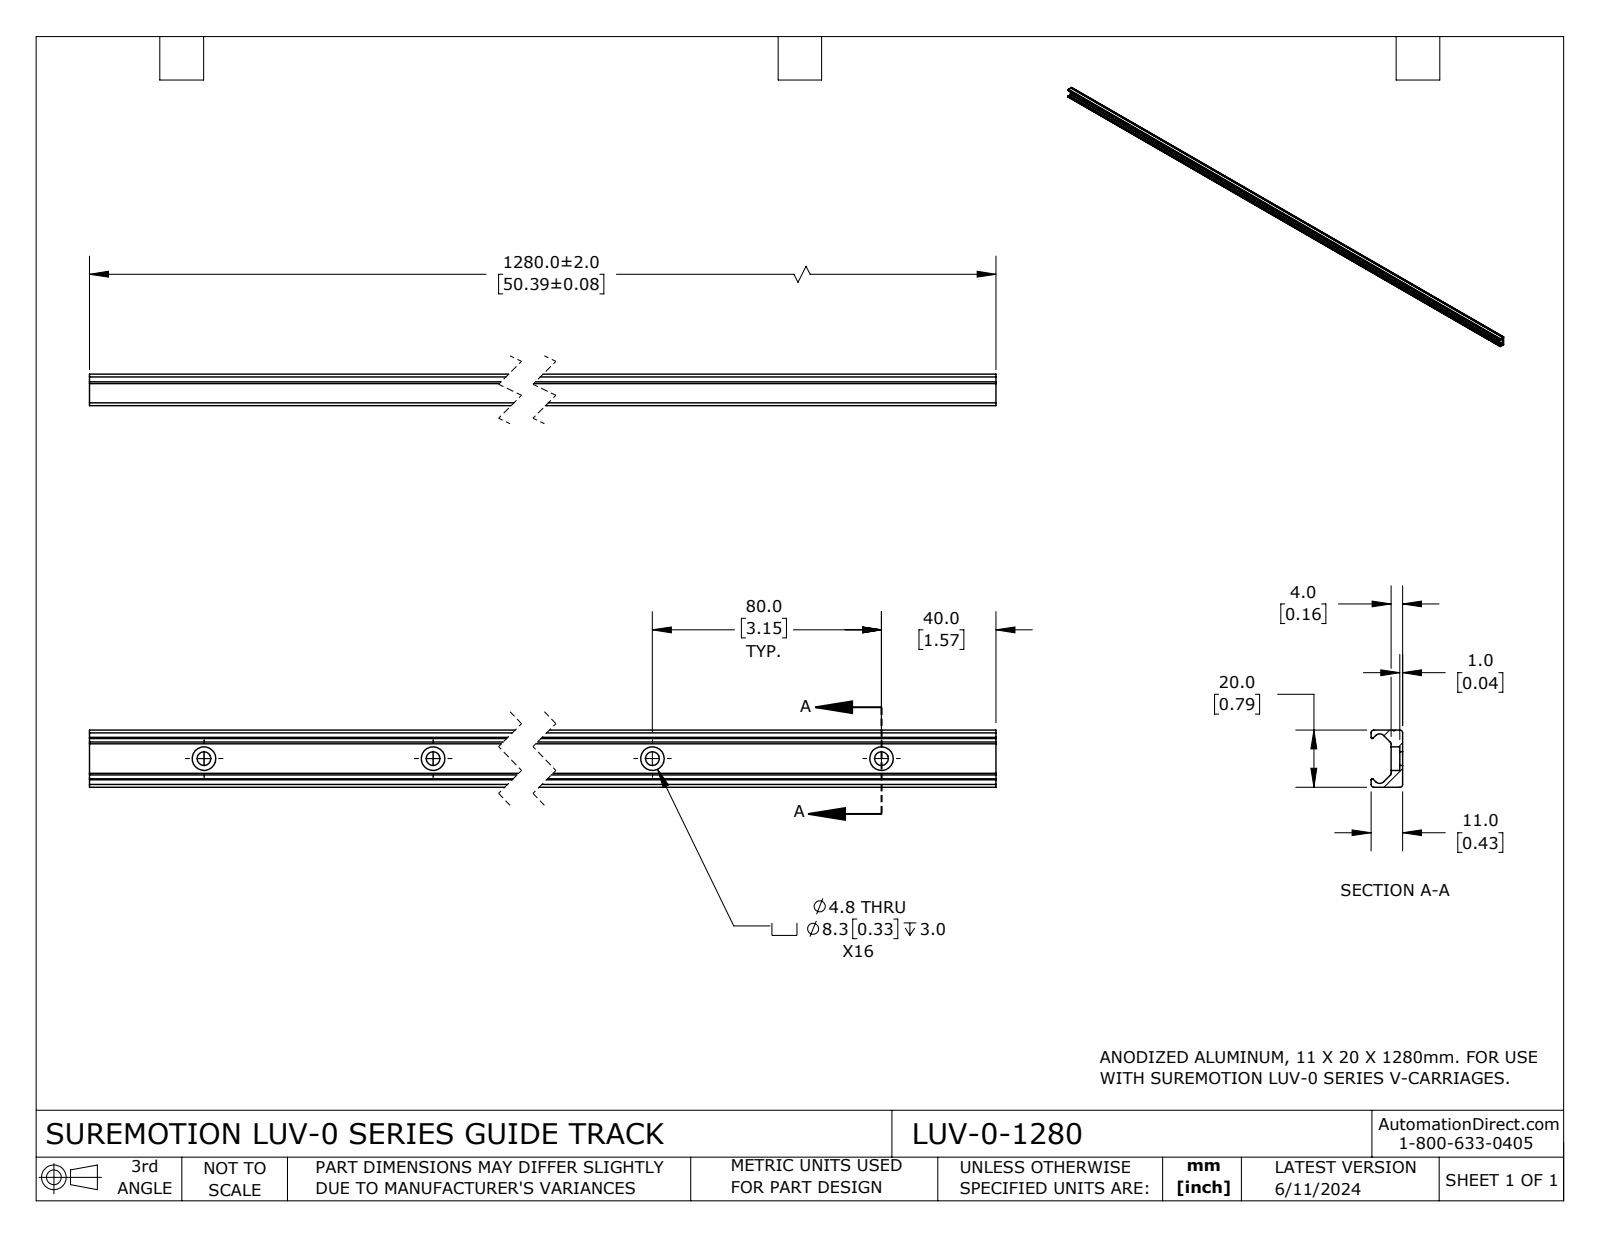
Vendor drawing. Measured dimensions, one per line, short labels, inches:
name: LUV-0-1280
written by: SolidWorks 2023 (CONFIG_CONTROL_DESIGN)
unit: in
bodies: 1 solid, 106 faces (29 planar, 77 cylindrical, 0 other)
size: 50.394 × 0.787 × 0.433
volume: 8.621 in³; area: 150.1 in²
holes: 16× ⌀0.189, 9× ⌀0.325, 7× ⌀0.325
rounds: 4× R0.039, 2× R0.015, 2× R0.016, 2× R0.031, 2× R0.078, 1× R0.013
face distances: 0.158, 0.787, 0.433, 0.275, 0.528, 0.04, 0.118, 0.393, 50.394
hole spacings: 3.15, 6.299, 9.449, 12.598, 15.748, 18.898, 22.047, 25.197
